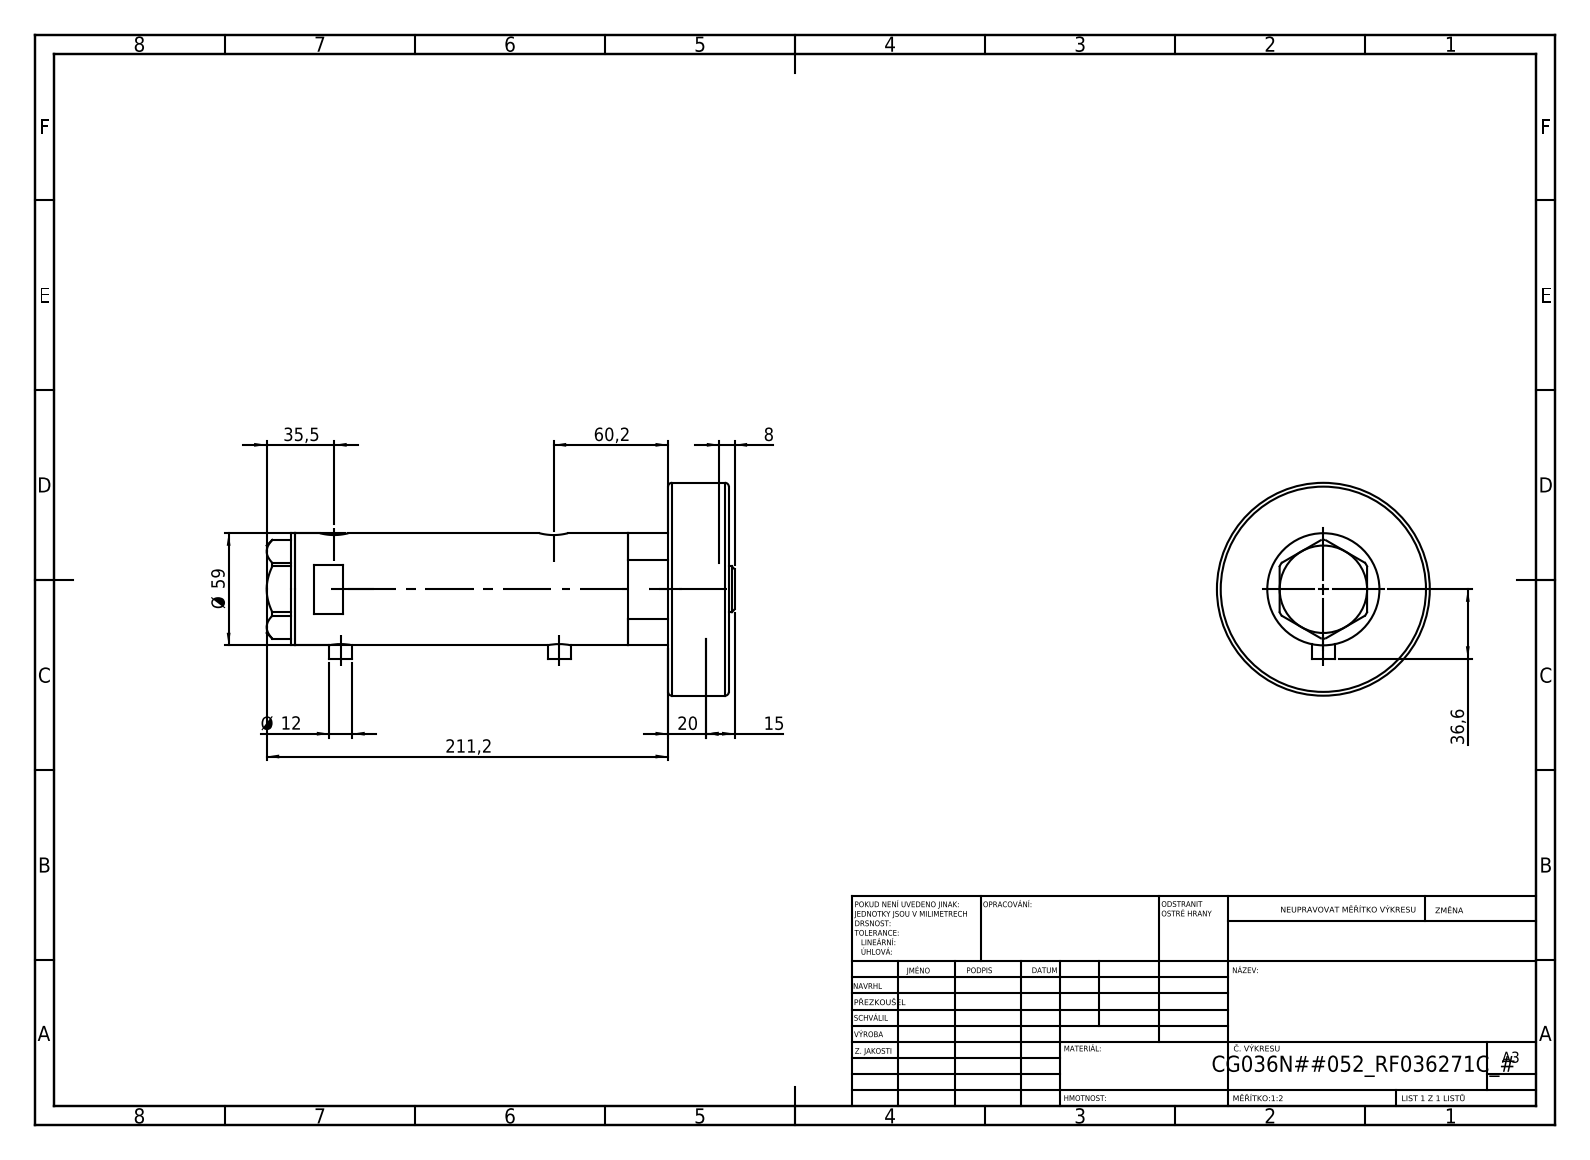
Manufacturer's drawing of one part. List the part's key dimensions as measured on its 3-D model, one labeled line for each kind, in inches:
Part name (STEP PRODUCT): V270CG_271C; V270CG_VC; V270CG_BACK; V270CG_FRONT (+1 more)
STEP written by: SolidWorks 2019 (CONFIG_CONTROL_DESIGN)
Units: inches
Bodies: 5 solids, 130 faces (53 planar, 53 cylindrical, 24 other)
Overall size (bounding box): 9.693 × 4.409 × 4.409
Volume: 50.64 in³ · Surface area: 226.1 in²
Round holes (diameter × count): ⌀0.383 ×2, ⌀0.492 ×2, ⌀0.591 ×2, ⌀0.335 ×1, ⌀0.984 ×1, ⌀1.043 ×1, ⌀1.417 ×1, ⌀1.575 ×1, ⌀1.89 ×1, ⌀2.047 ×1
Round bosses / shafts (diameter × count): ⌀0.472 ×2, ⌀4.409 ×1, ⌀2.323 ×1, ⌀1.811 ×1, ⌀0.945 ×1
Main face-to-face distances: 1.26, 7.724, 8.984, 5.402, 2.323, 3.583, 0.925, 4.476, 6.799, 8.059
Hole centre spacings: 0.114, 0.138, 4.409, 4.524, 4.547, 4.661
